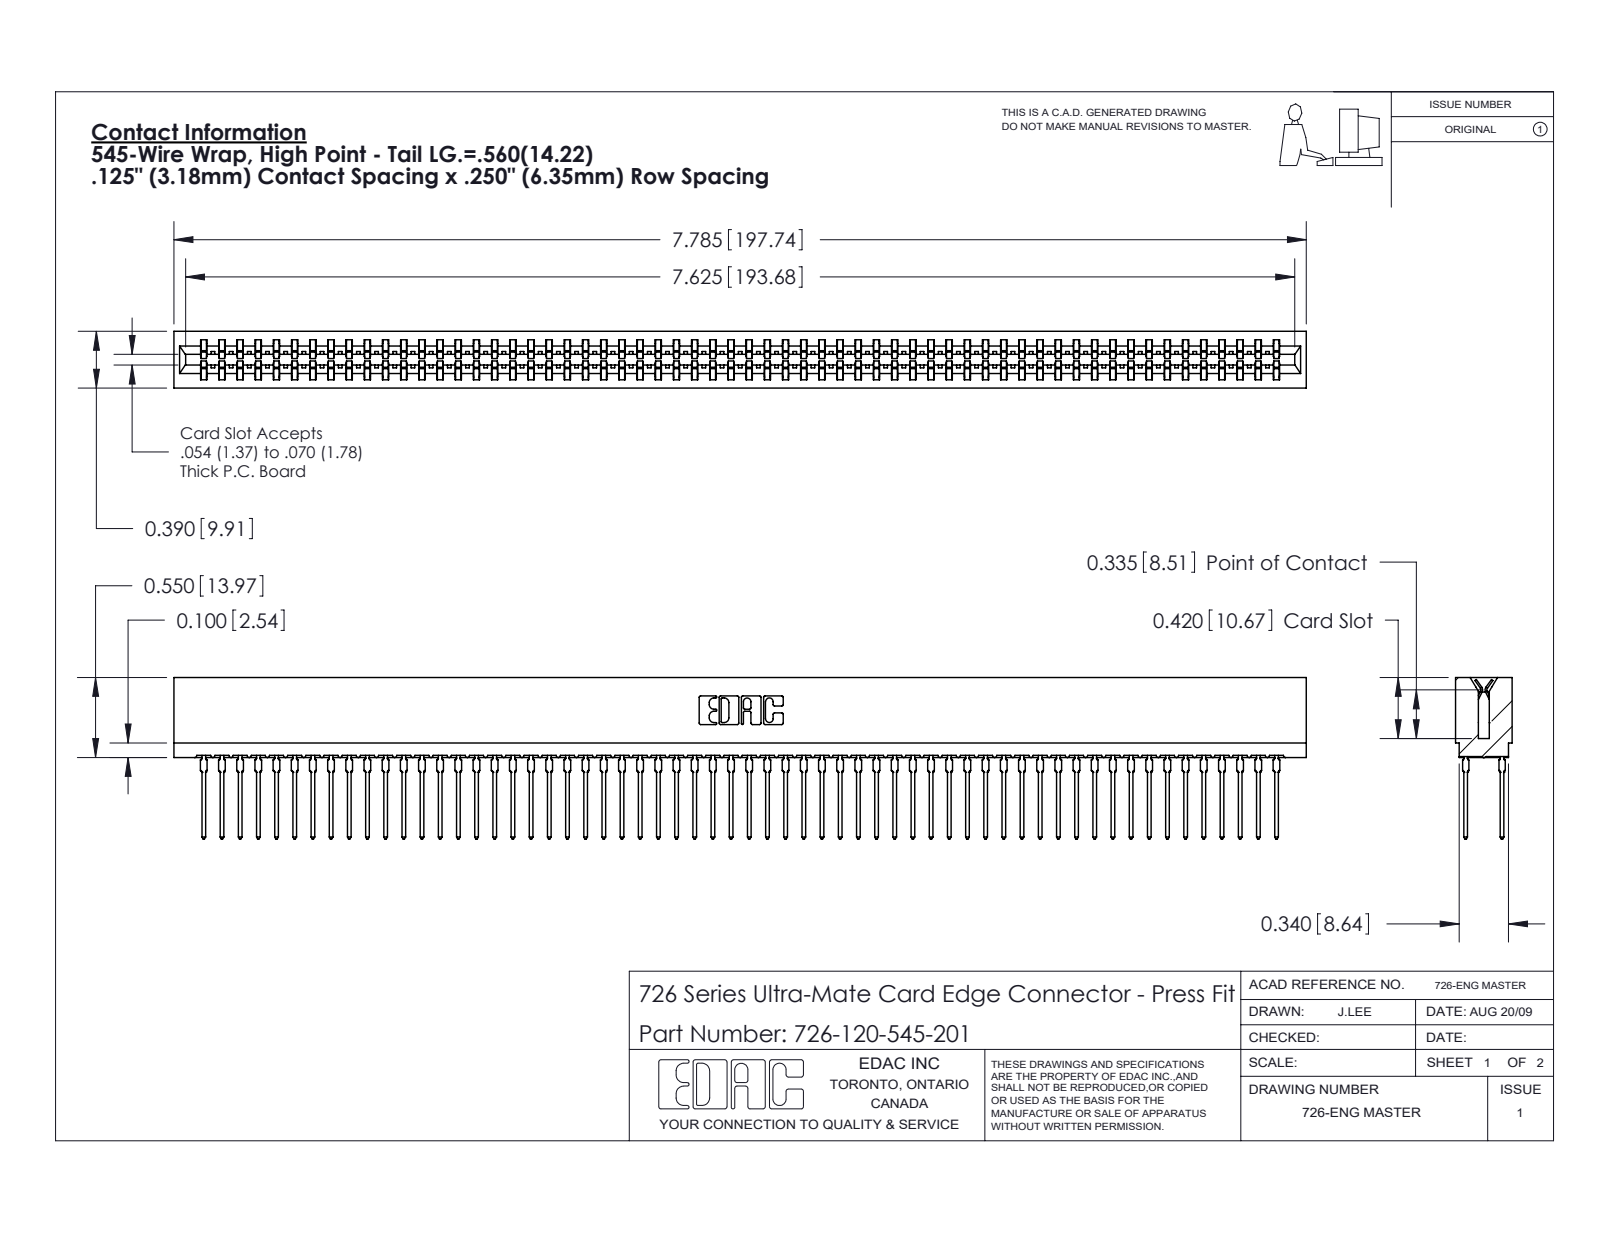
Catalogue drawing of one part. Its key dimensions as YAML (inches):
part_name: "726 Part_.515 Slot Depth - 01; 746-292-001_545; 726-120-545-201"
step_written_by: "SolidWorks 2020 (CONFIG_CONTROL_DESIGN)"
units: inches
bodies: {solids: 121, faces: 10837, planar: 5575, cylindrical: 2142, other: 3120}
overall_size: [7.785, 1.109, 0.39]
volume: 1.13
surface_area: 51.29
partial_cylinders:
  - {radius: 0.021, count: 240}
  - {radius: 0.015, count: 61}
  - {radius: 0.01, count: 22}
  - {radius: 0.005, count: 8}
  - {radius: 0.011, count: 8}
  - {radius: 0.007, count: 6}
  - {radius: 0.031, count: 6}
  - {radius: 0.026, count: 3}
face_to_face_distances: [0.057, 0.333, 0.025, 0.307, 0.25, 0.39, 0.083, 0.275, 0.365, 0.032]
